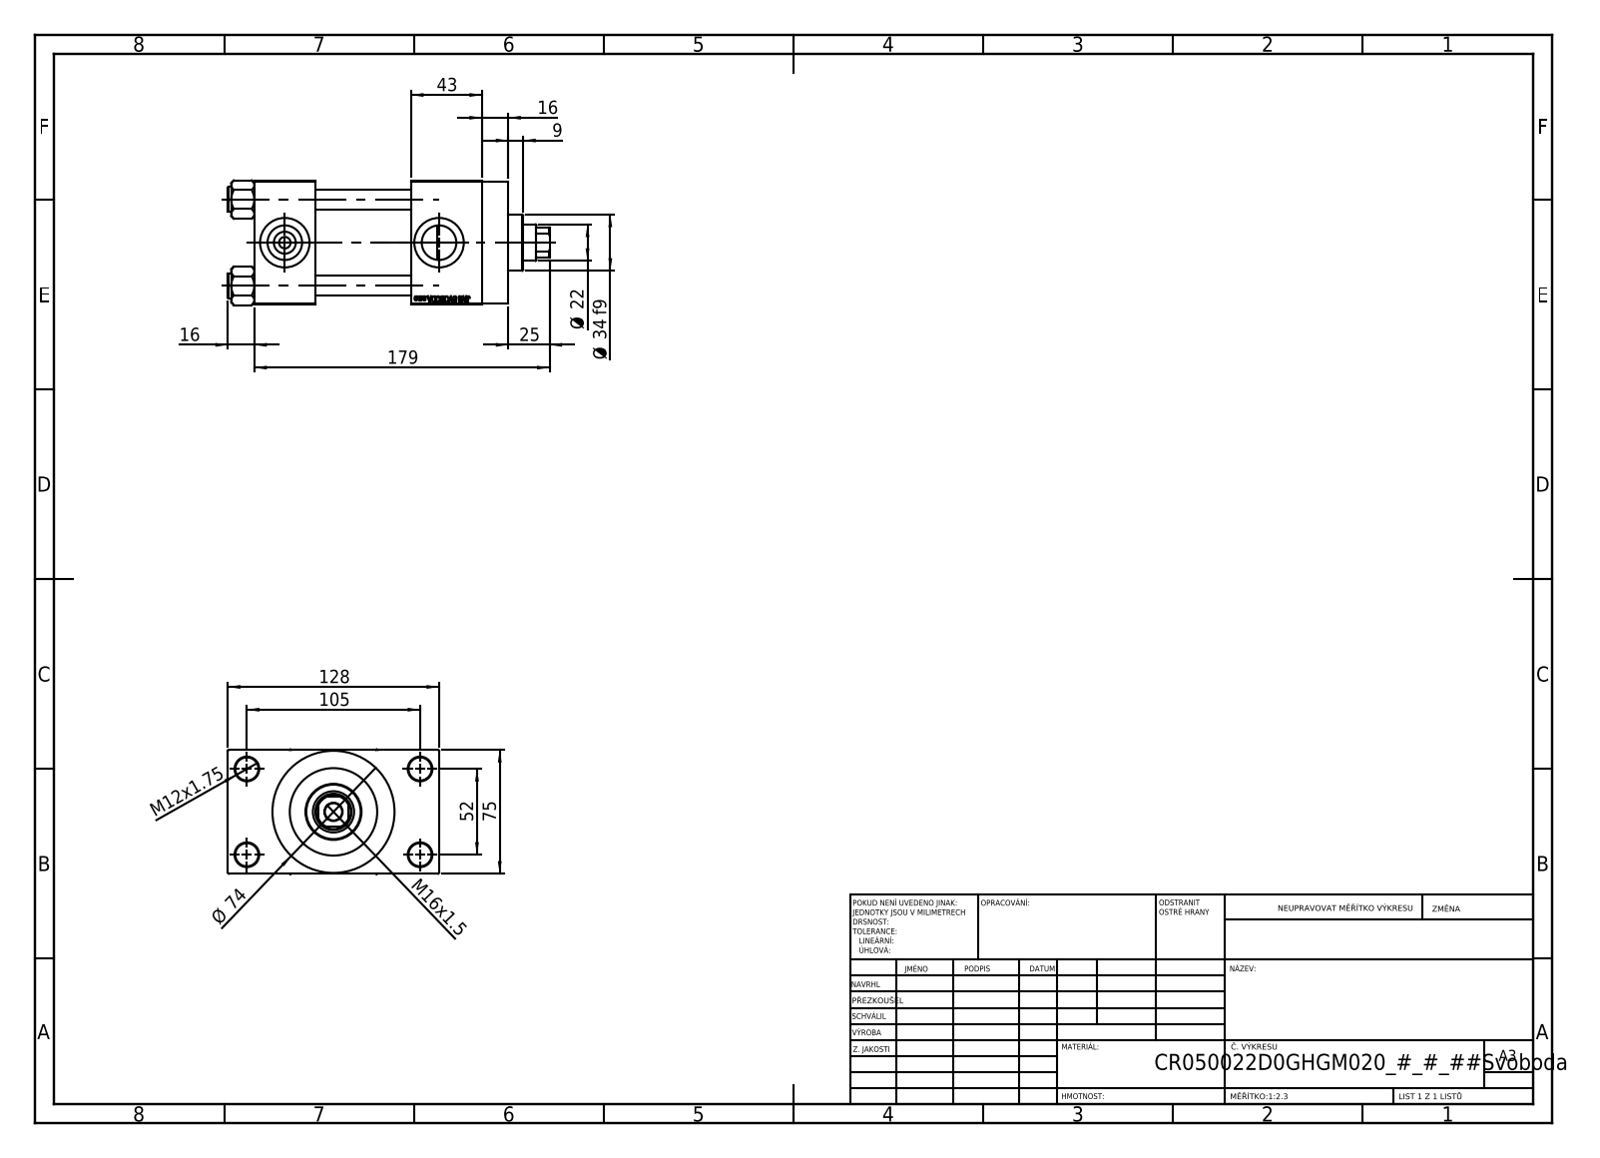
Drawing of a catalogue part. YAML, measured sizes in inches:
part_name: "V215_VC_A; NUT_M5_D; V215CR_VCP_D; V215CR_D_TYCINKA (+1 more)"
step_written_by: "SolidWorks 2019 (CONFIG_CONTROL_DESIGN)"
units: inches
bodies: {solids: 11, faces: 1103, planar: 497, cylindrical: 88, other: 518}
overall_size: [7.677, 5.039, 2.974]
volume: 48.67
surface_area: 258.4
round_holes:
  - {diameter: 0.472, count: 4}
  - {diameter: 0.551, count: 4}
  - {diameter: 0.276, count: 2}
  - {diameter: 0.825, count: 2}
  - {diameter: 1.181, count: 2}
  - {diameter: 0.413, count: 1}
  - {diameter: 0.866, count: 1}
  - {diameter: 0.984, count: 1}
  - {diameter: 1.614, count: 1}
  - {diameter: 1.969, count: 1}
  - {diameter: 2.087, count: 1}
round_bosses_or_shafts:
  - {diameter: 0.591, count: 4}
  - {diameter: 2.913, count: 1}
  - {diameter: 2.205, count: 1}
  - {diameter: 1.339, count: 1}
partial_cylinders:
  - {radius: 0.413, count: 1}
face_to_face_distances: [2.953, 2.283, 1.457, 3.74, 1.043, 5.433, 3.976, 1.693, 3.996, 0.63]
hole_center_spacings: [1.037, 1.456, 2.059, 2.3, 2.307, 3.096, 3.715, 2.047]
